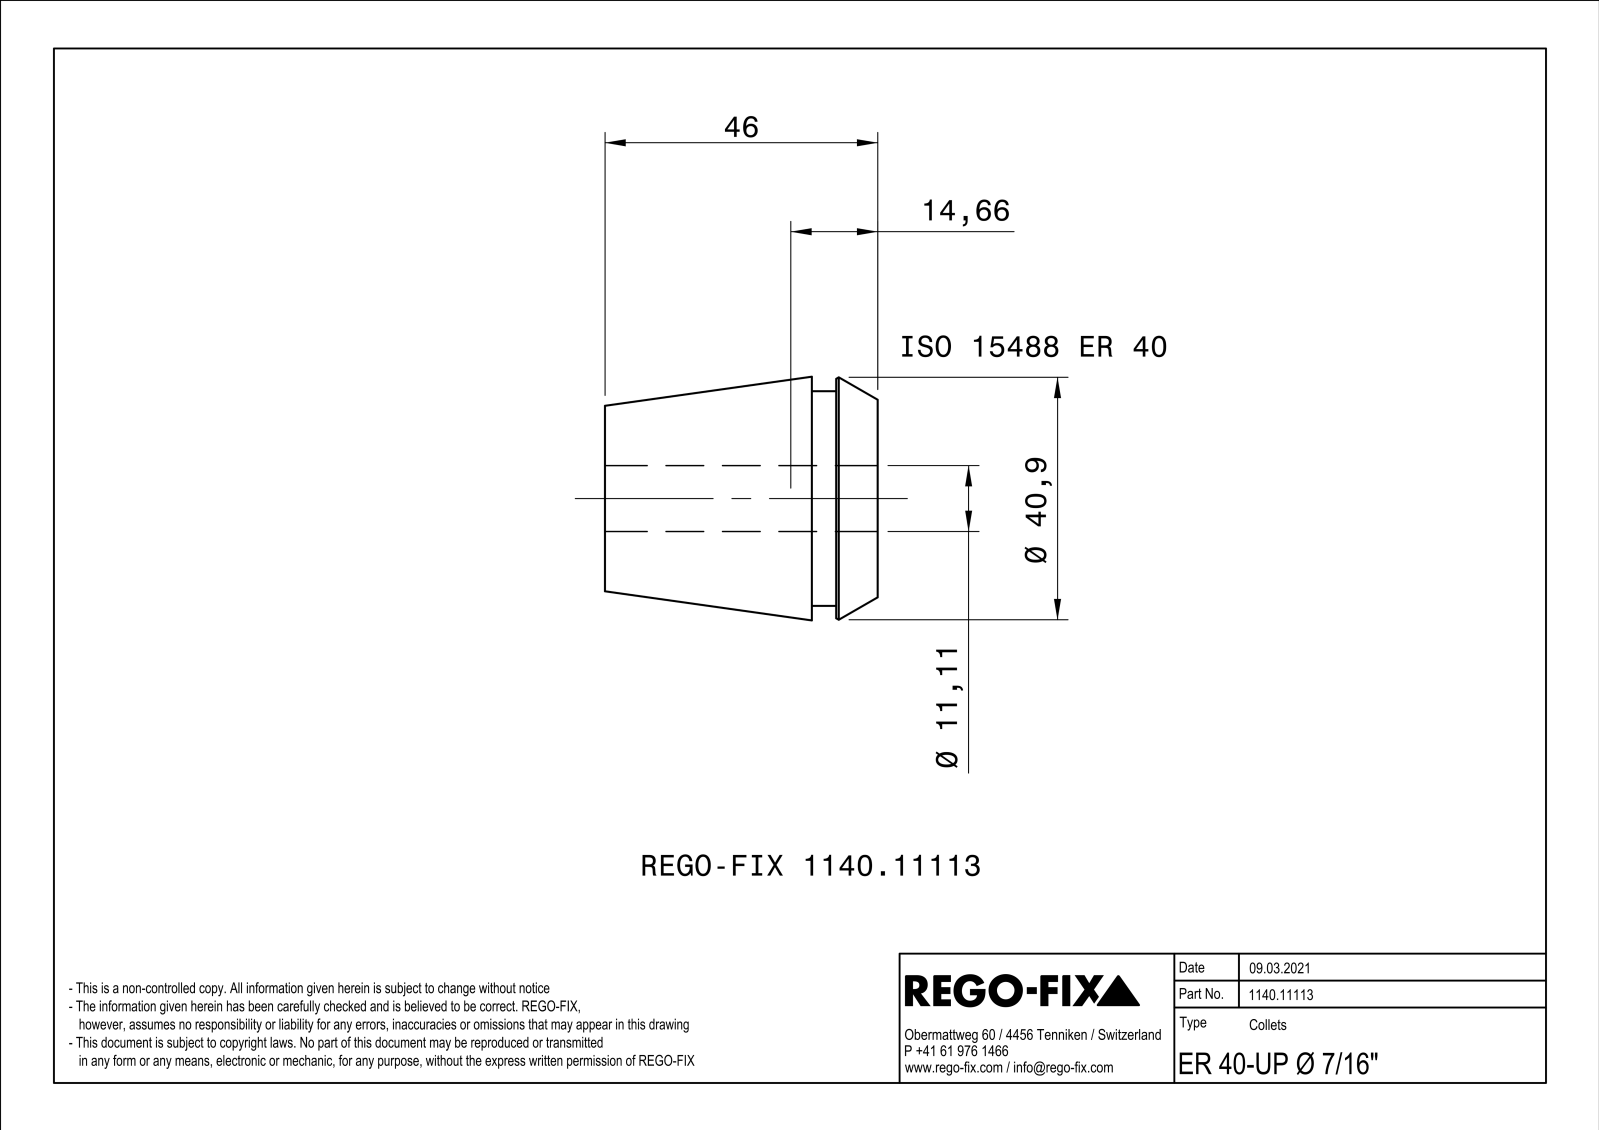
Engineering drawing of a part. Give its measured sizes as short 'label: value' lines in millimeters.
name: NOCUT
written by: SIEMENS PLM Software Solid Edge ST10 (AUTOMOTIVE_DESIGN)
unit: mm
bodies: 1 solid, 177 faces (88 planar, 9 cylindrical, 80 other)
size: 46 × 40.99 × 40.99
volume: 35 177 mm³; area: 24 014 mm²
holes: 1× ⌀11.11
bosses: 1× ⌀36.2
face distances: 1, 46, 11.1, 34.9, 7, 4.1, 39, 7.5, 0.5, 3.6
